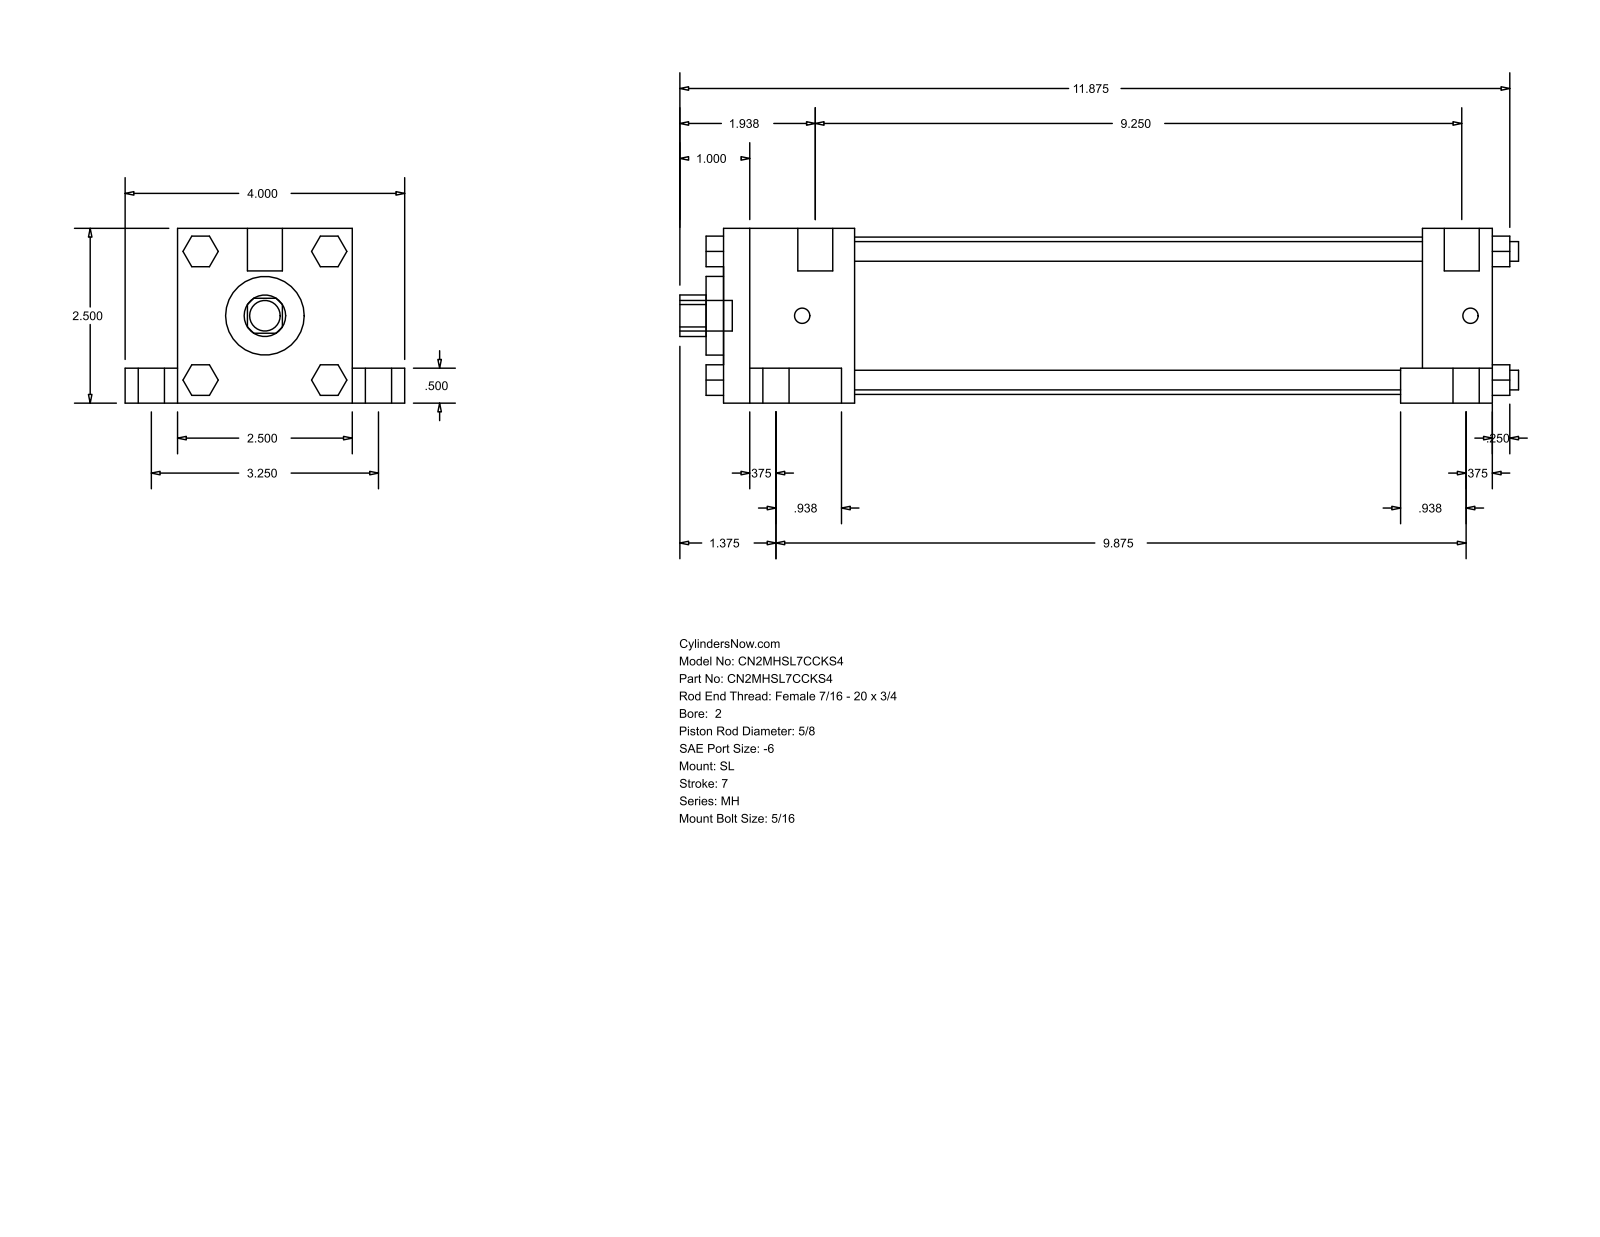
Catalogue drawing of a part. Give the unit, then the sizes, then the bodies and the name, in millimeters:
Units: millimetres
Overall size (bounding box): 304.8 × 101.6 × 63.5
Round holes (diameter × count): ⌀15.88 ×1, ⌀28.57 ×1, ⌀57.15 ×1
Round bosses / shafts (diameter × count): ⌀15.88 ×4, ⌀9.53 ×4, ⌀7.14 ×4, ⌀5.56 ×4, ⌀12.7 ×2, ⌀11.11 ×1
Partial cylindrical surfaces — rounded edges, fillets, slot ends (radius × count): R7.54 ×1
Main face-to-face distances: 63.5, 279.39, 12.7, 19.05, 50.8, 82.55, 254, 25.39, 47.62, 206.38
Bodies: 0 solids, 148 faces (112 planar, 36 cylindrical, 0 other)
Part name (STEP PRODUCT): MH_SL__0200_0.625
STEP written by: GSSL Pune (CONFIG_CONTROL_DESIGN)
